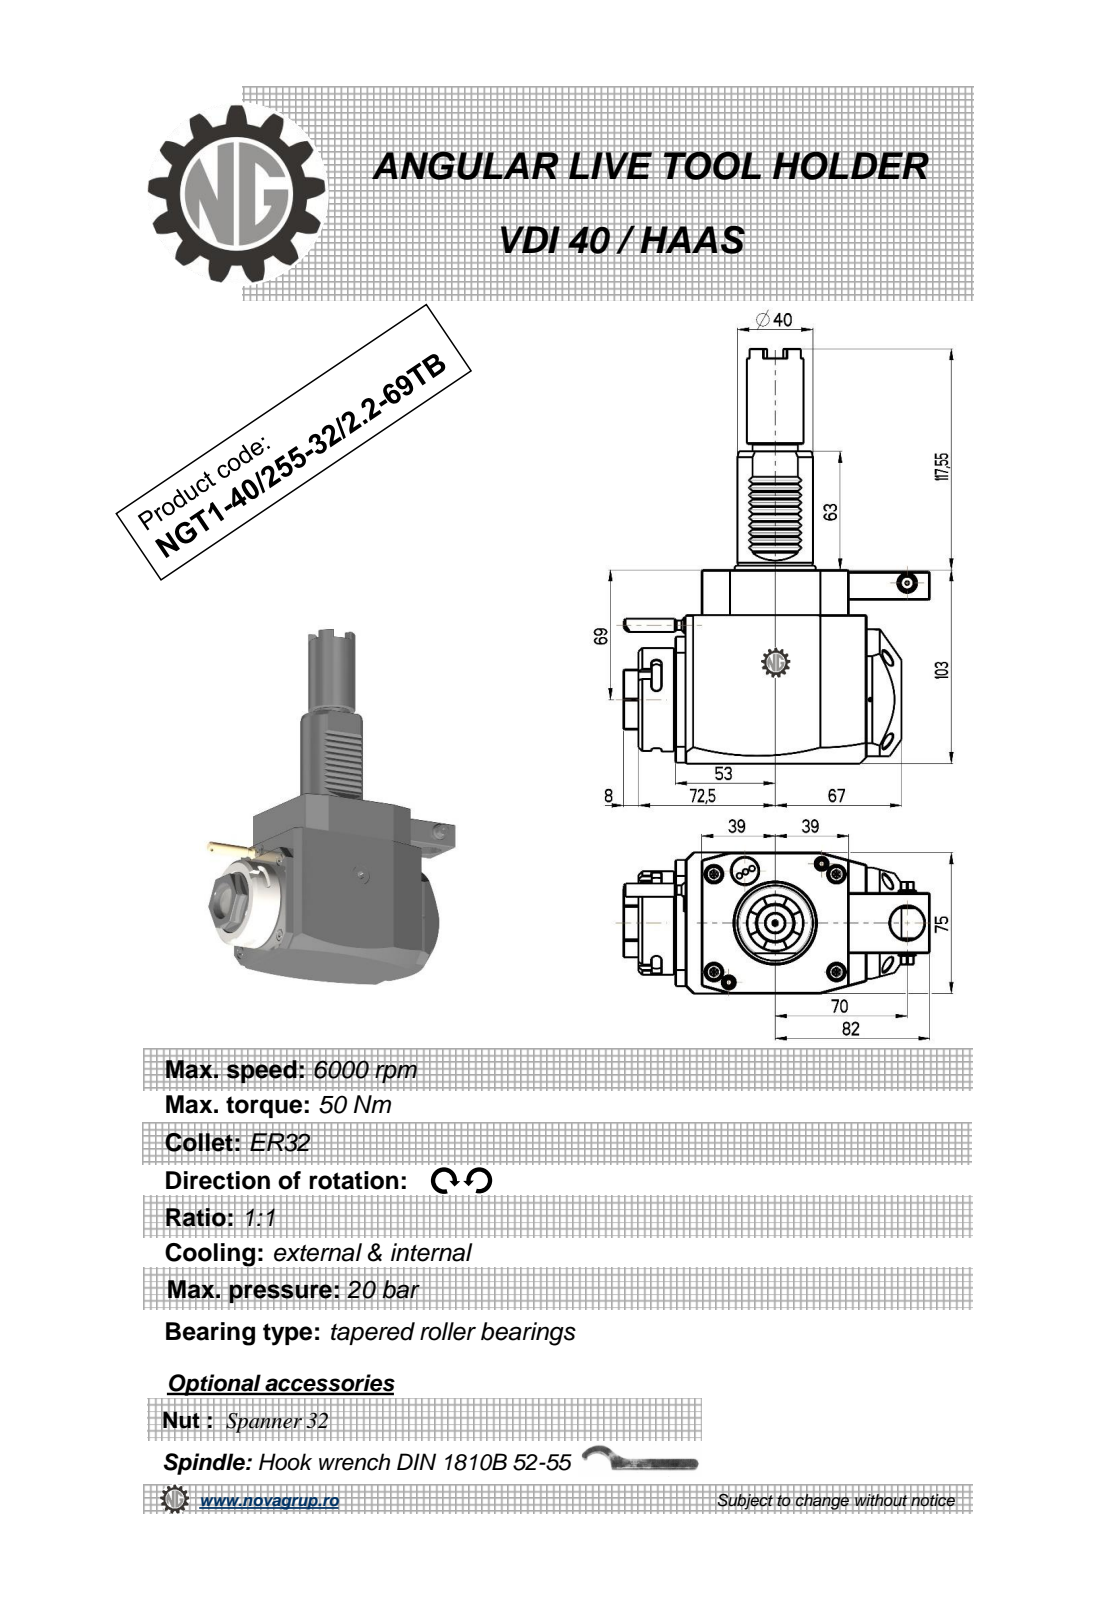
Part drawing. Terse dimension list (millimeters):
name: NGT1_40_255_32_1_2_69TB
written by: PRO/ENGINEER BY PARAMETRIC TECHNOLOGY CORPORATION, 2010280 (CONFIG_CONTROL_DESIGN)
unit: mm
bodies: 1 solid, 393 faces (219 planar, 86 cylindrical, 88 other)
size: 220.55 × 162.5 × 75
volume: 941 456 mm³; area: 75 539 mm²
holes: 1× ⌀2, 1× ⌀2.5, 1× ⌀3, 1× ⌀9.5, 1× ⌀18, 1× ⌀20, 1× ⌀23
bosses: 2× ⌀8.96, 1× ⌀55, 1× ⌀48, 1× ⌀40, 1× ⌀30, 1× ⌀24, 1× ⌀10, 1× ⌀7
rounds: 10× R0.3, 6× R2.5, 2× R180, 1× R0.5, 1× R3.85, 1× R4.25, 1× R24.5, 1× R37.5
face distances: 75, 103, 33.5, 19.5, 79, 8, 14, 102, 21.5, 87
hole spacings: 28.11, 43.2, 61.5, 70
